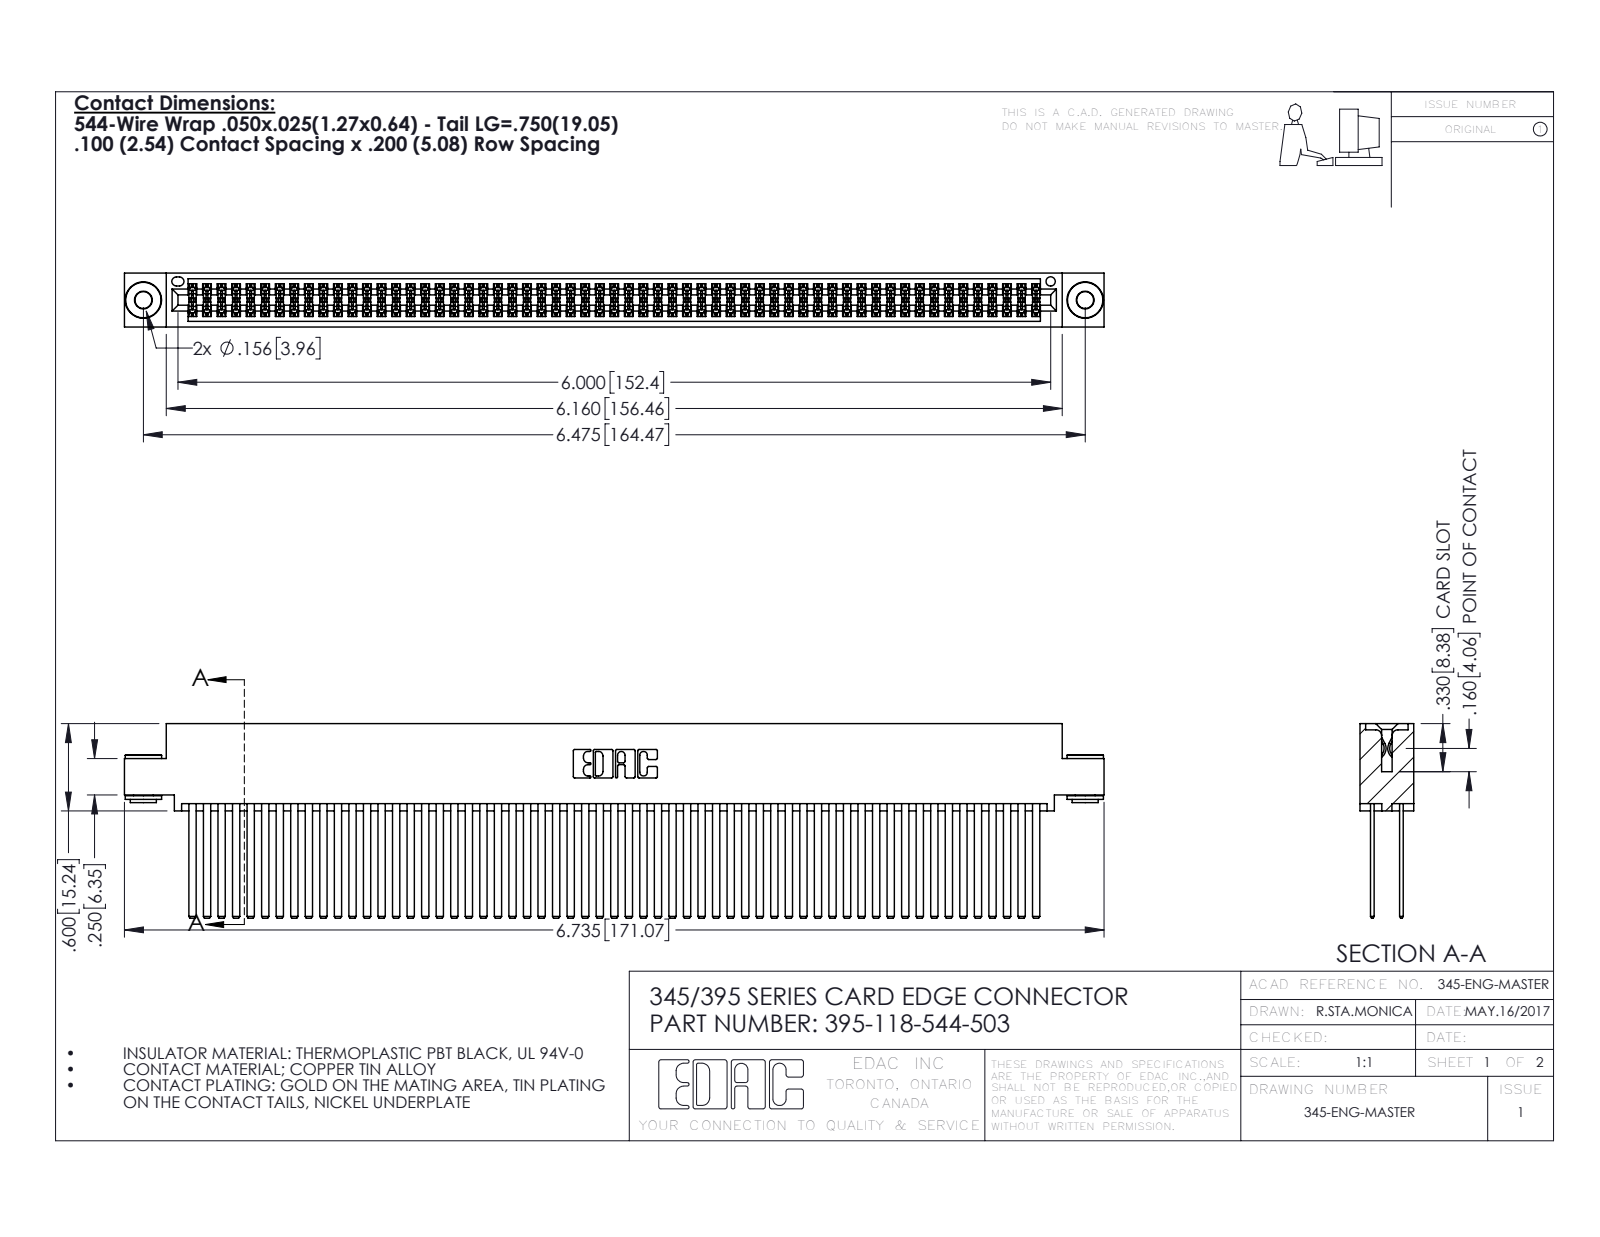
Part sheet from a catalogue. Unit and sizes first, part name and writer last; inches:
Units: inches
Overall size (bounding box): 6.735 × 1.337 × 0.37
Round holes (diameter × count): ⌀0.116 ×2, ⌀0.156 ×2, ⌀0.064 ×1
Round bosses / shafts (diameter × count): ⌀0.25 ×2, ⌀0.18 ×2, ⌀0.136 ×2
Partial cylindrical surfaces — rounded edges, fillets, slot ends (radius × count): R0.006 ×177, R0.01 ×22, R0.007 ×6, R0.031 ×6, R0.026 ×3, R0.014 ×2, R0.019 ×2, R0.022 ×2
Main face-to-face distances: 0.2, 0.025, 0.072, 0.098, 0.272, 0.298, 0.225, 0.175, 0.37, 0.05
Hole centre spacings: 0.27, 6.239, 6.475
Volume: 1.121 in³ · Surface area: 50.59 in²
Bodies: 121 solids, 5360 faces (3516 planar, 1836 cylindrical, 8 other)
Part name (STEP PRODUCT): 345-292-001_345-293-144; 345-250-002_345-250-002-102; 395-118-544-503; 345 Part_0.110 Offset - 0.156 Dia-TH
STEP written by: SolidWorks 2016 (CONFIG_CONTROL_DESIGN)
